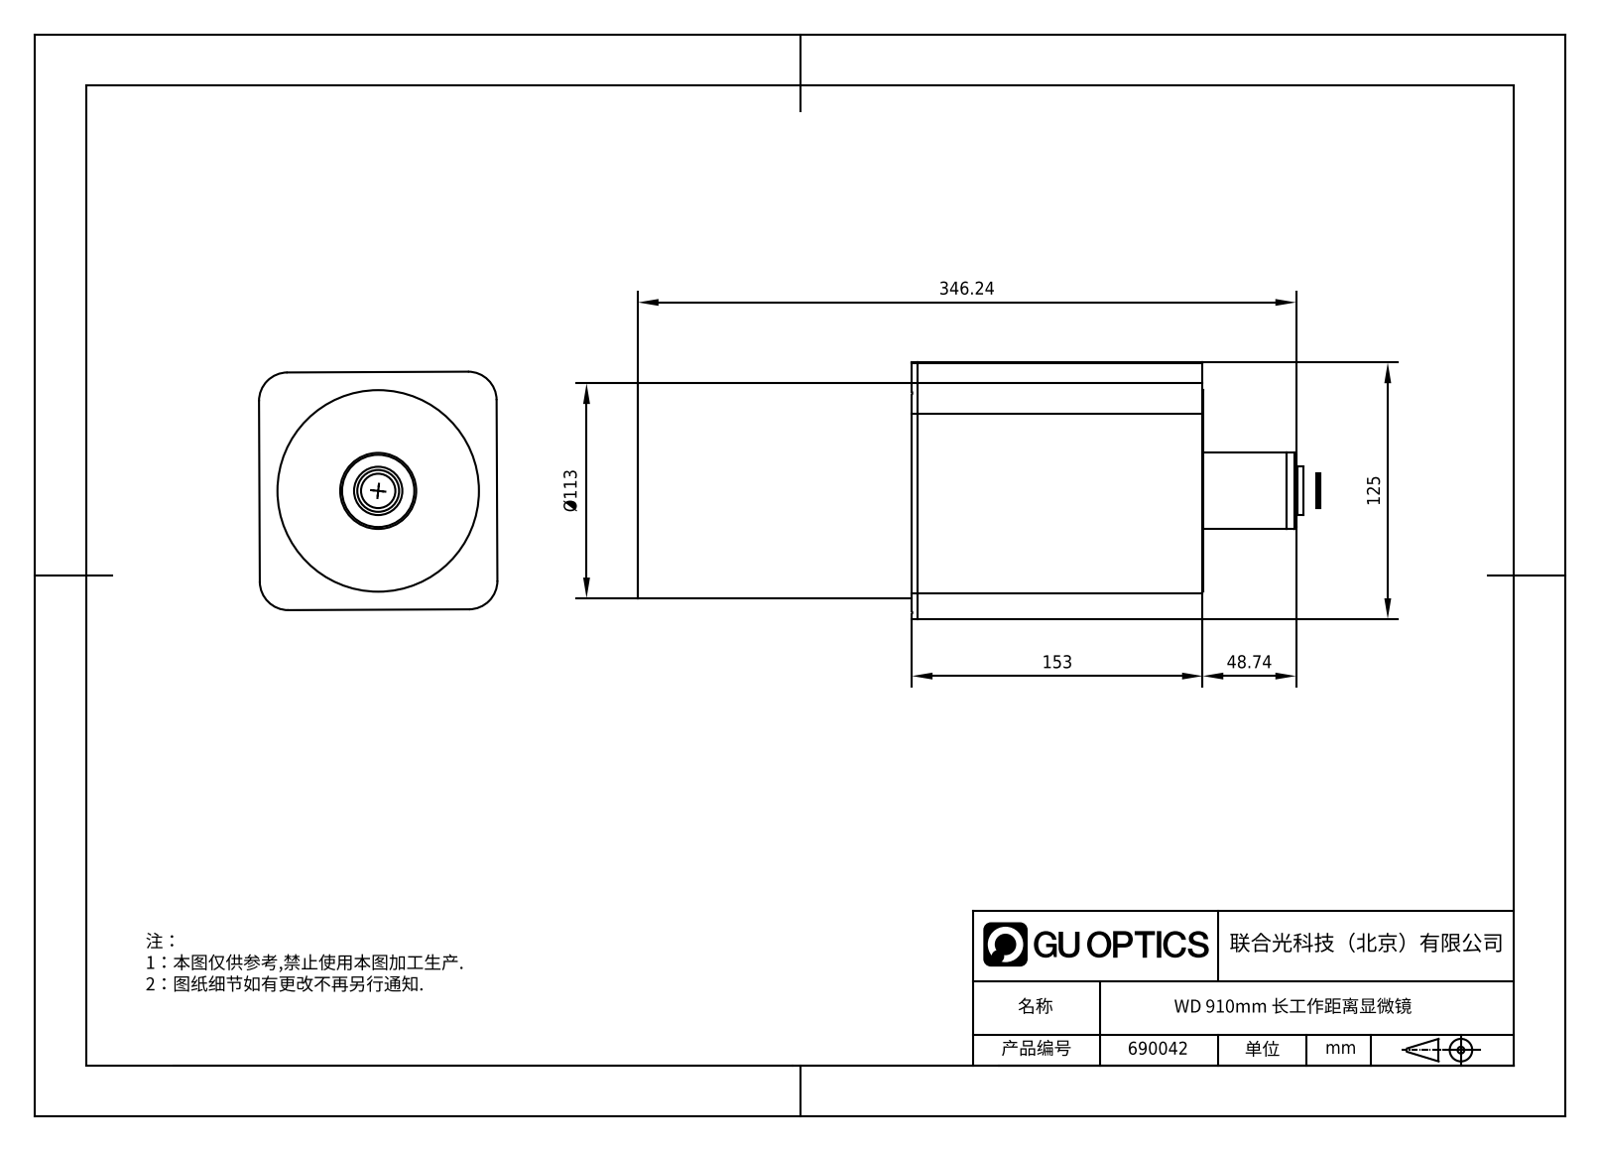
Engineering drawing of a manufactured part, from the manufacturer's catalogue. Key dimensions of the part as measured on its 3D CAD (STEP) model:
Part name (STEP PRODUCT): 690042
STEP written by: SolidWorks 2020 (CONFIG_CONTROL_DESIGN)
Units: millimetres
Bodies: 17 solids, 1229 faces (331 planar, 372 cylindrical, 526 other)
Overall size (bounding box): 358.78 × 134.84 × 134.84
Volume: 1 020 000 mm³ · Surface area: 569 627 mm²
Round holes (diameter × count): ⌀2.5 ×14, ⌀3.3 ×4, ⌀3.4 ×4, ⌀1.25 ×2, ⌀2 ×2, ⌀2.1 ×2, ⌀3.2 ×2, ⌀4.5 ×2, ⌀22 ×1, ⌀24 ×1, ⌀27.07 ×1, ⌀28 ×1
Round bosses / shafts (diameter × count): ⌀119 ×1, ⌀113 ×1, ⌀112.75 ×1, ⌀111 ×1, ⌀100.8 ×1, ⌀100 ×1, ⌀40 ×1, ⌀33 ×1
Partial cylindrical surfaces — rounded edges, fillets, slot ends (radius × count): R5 ×8, R1 ×6, R0.5 ×4, R3 ×4, R15 ×4, R2.05 ×2, R1.5 ×1, R2.25 ×1
Main face-to-face distances: 125.01, 122.03, 2.98, 3.03, 121.98, 119, 150, 3, 5.85, 2.35
Hole centre spacings: 112, 79.19, 80, 3.01, 12, 60.17, 60.47, 100.32
